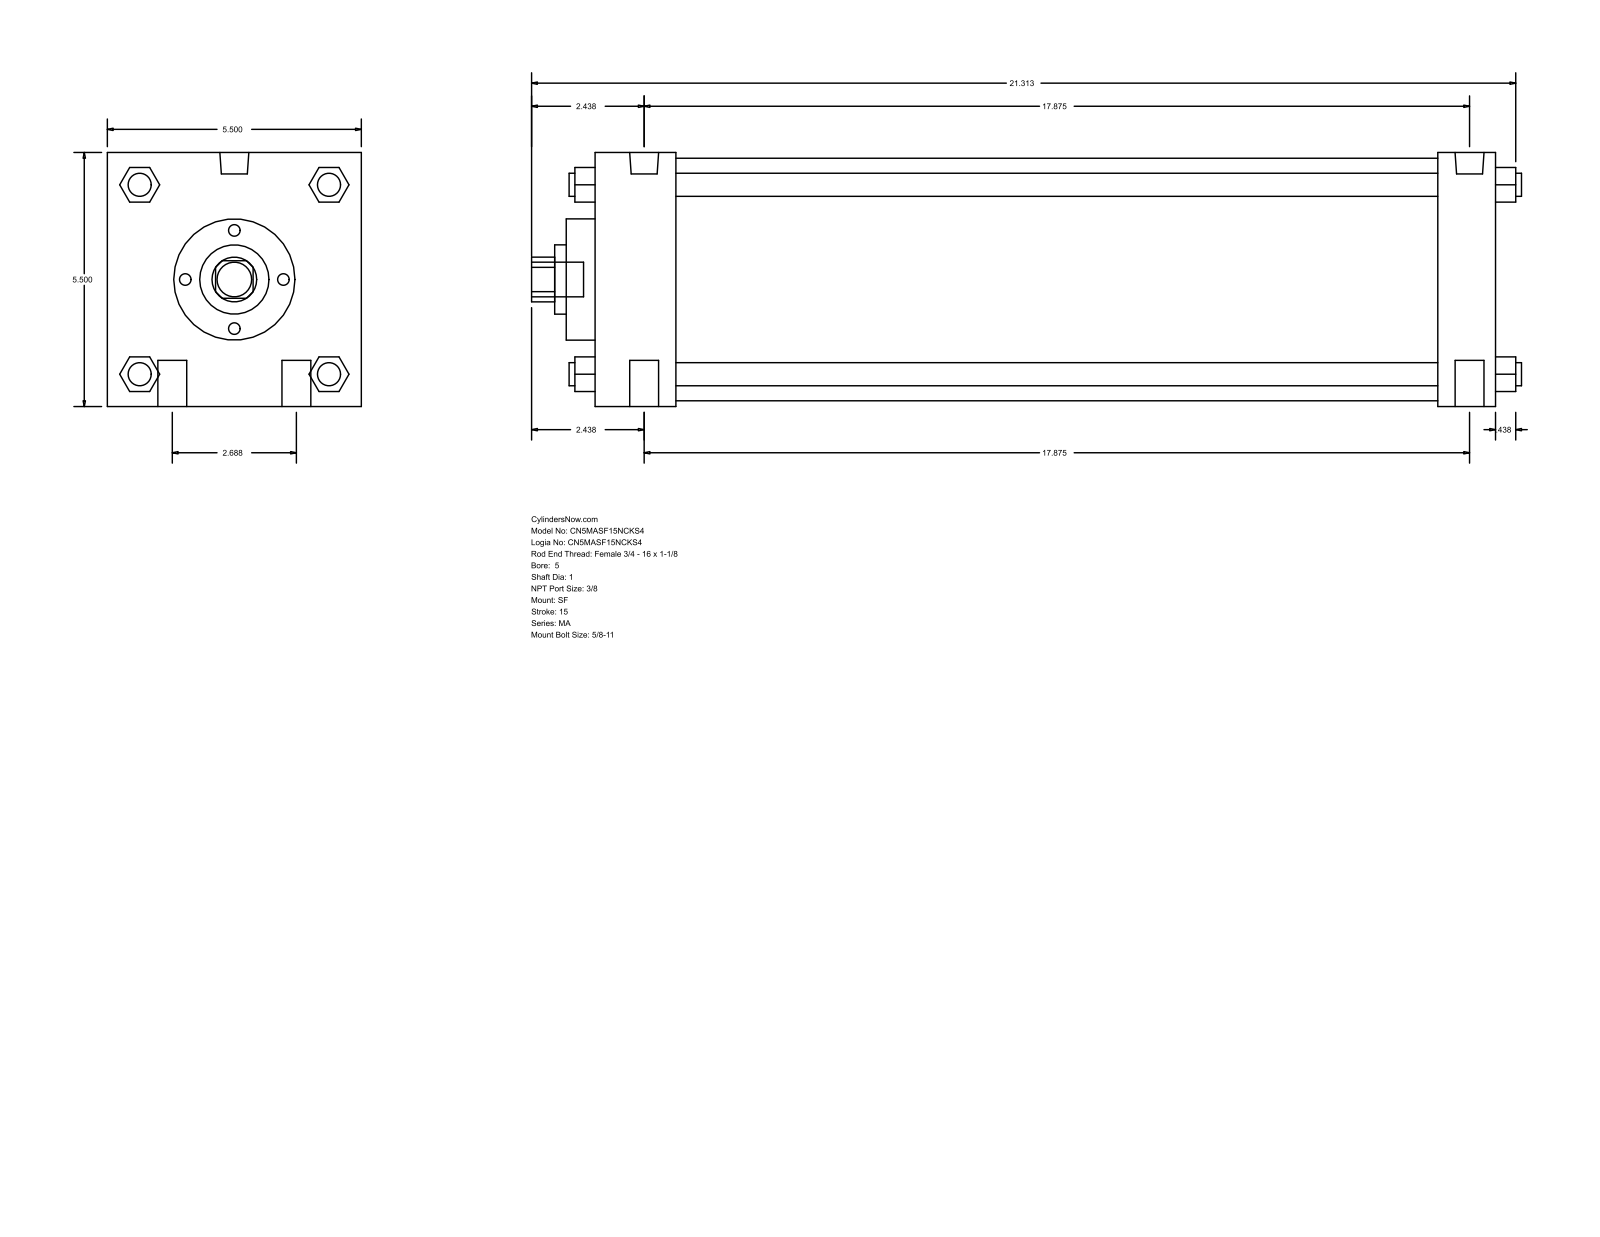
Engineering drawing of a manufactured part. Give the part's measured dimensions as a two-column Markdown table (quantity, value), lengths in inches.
| quantity | value |
| --- | --- |
| part name | MA_SF__0500_1 |
| STEP written by | GSSL Pune (CONFIG_CONTROL_DESIGN) |
| units | inches |
| bodies | 0 solids, 126 faces (95 planar, 31 cylindrical, 0 other) |
| overall size | 21.437 × 5.5 × 5.5 |
| round holes (diameter × count) | 1 × 1, 1.5 × 1, 2.625 × 1, 5.25 × 1 |
| round bosses / shafts (diameter × count) | 0.625 × 4, 0.5 × 4, 0.627 × 2, 0.437 × 2, 0.75 × 1 |
| partial cylindrical surfaces (radius × count) | 0.484 × 1 |
| main face-to-face distances | 5.5, 19.5, 1.75, 18.25, 16.5, 17.75, 1.25, 0.625, 2.375, 18.875 |
